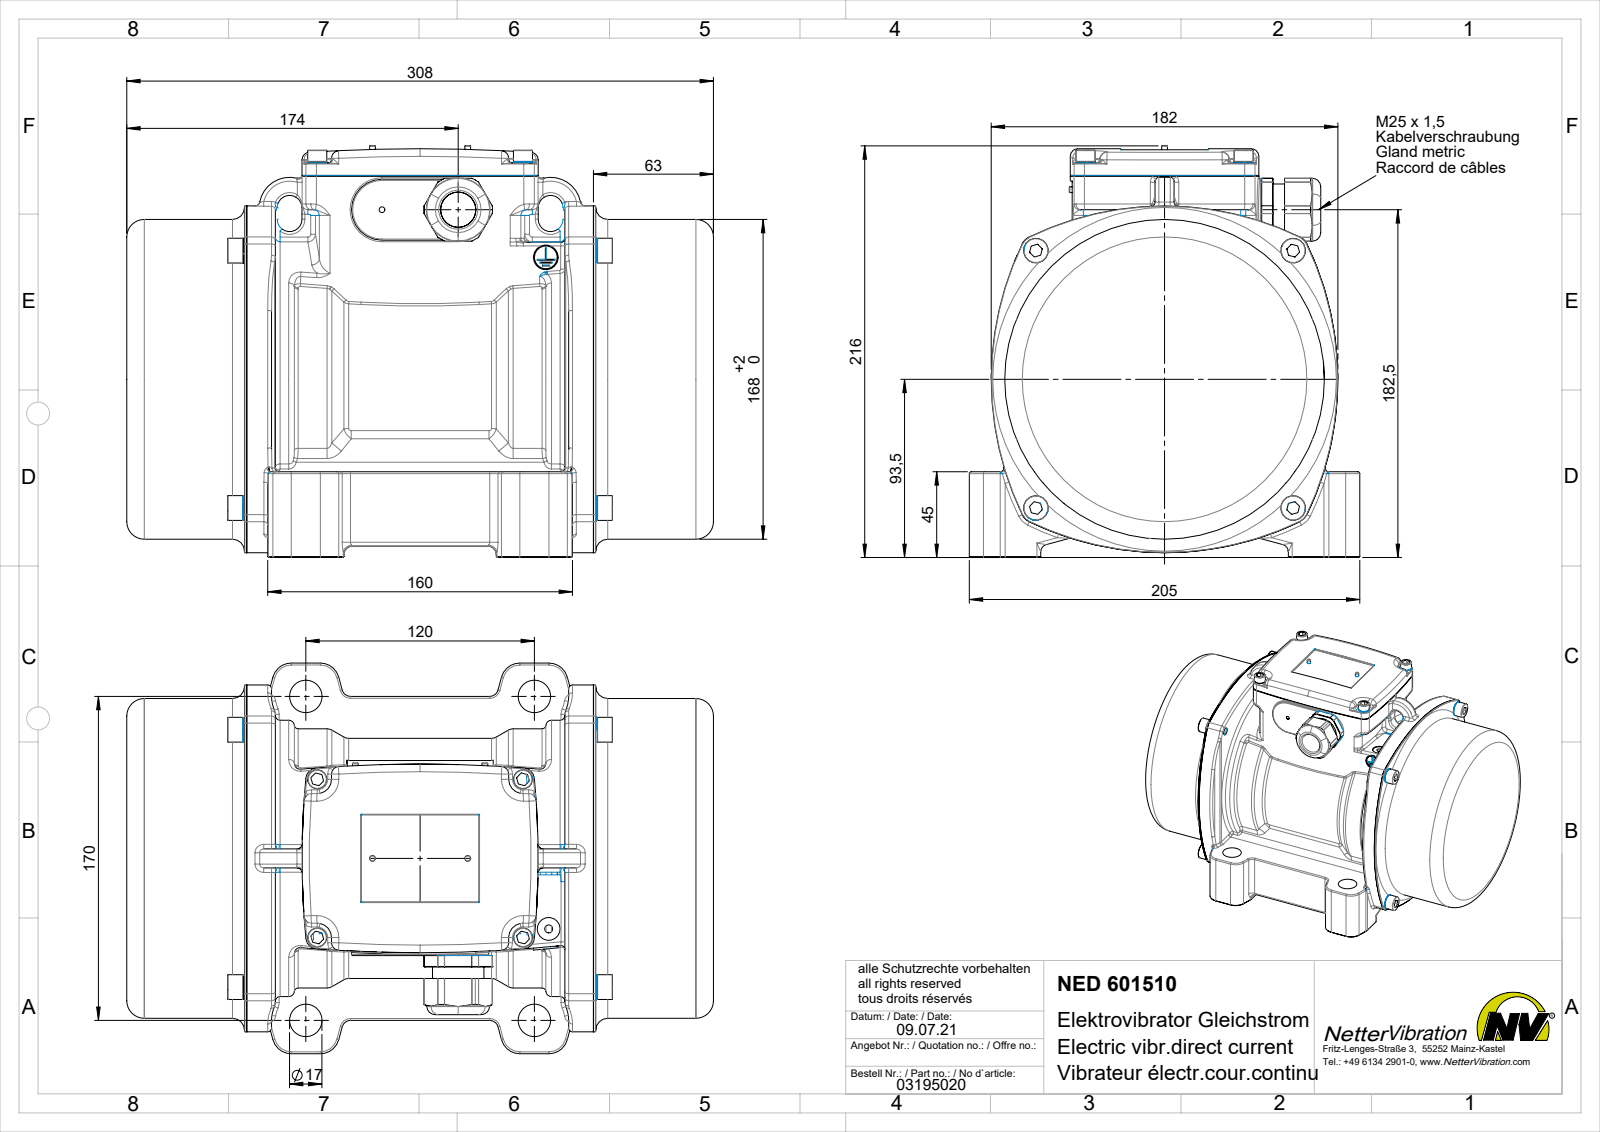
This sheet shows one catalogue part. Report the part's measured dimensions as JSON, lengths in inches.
{"part_name": "NED 601510", "step_written_by": "SolidWorks 2015 (AUTOMOTIVE_DESIGN)", "units": "inches", "bodies": {"solids": 0, "faces": 1519, "planar": 423, "cylindrical": 0, "other": 1096}, "overall_size": [12.126, 8.504, 8.071], "face_to_face_distances": [12.126, 0.236, 2.48, 9.646, 0.591, 3.071, 6.575, 9.055, 1.772, 2.008]}
